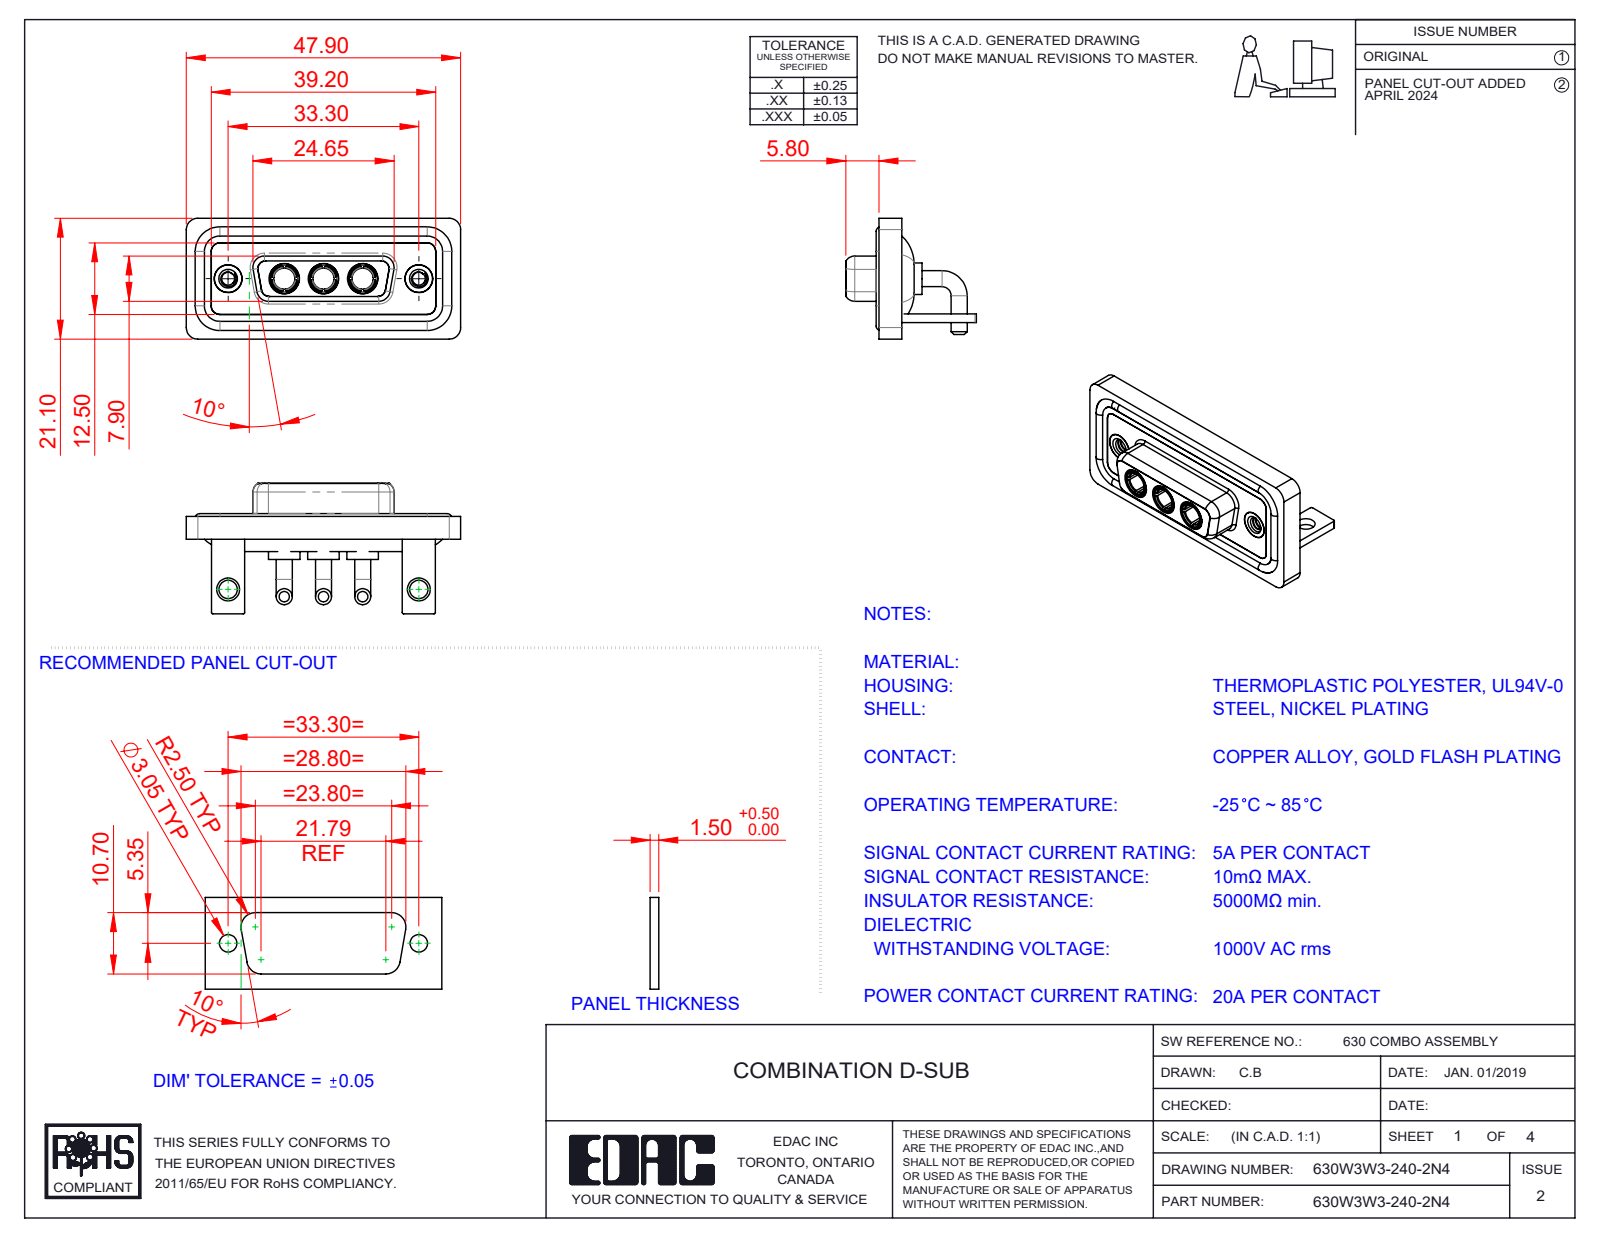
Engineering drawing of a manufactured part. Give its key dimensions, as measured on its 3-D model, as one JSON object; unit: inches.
{"part_name": "630Combo Shell Front_15 Contacts; 630Combo Threaded Rivet_2; 630Combo Housing_3W3; 630Combo Stabilizer Bracket_50 Contacts (+4 more)", "step_written_by": "SolidWorks 2023 (CONFIG_CONTROL_DESIGN)", "units": "inches", "bodies": {"solids": 15, "faces": 668, "planar": 212, "cylindrical": 287, "other": 169}, "overall_size": [1.886, 0.898, 0.831], "volume_in3": 0.399, "surface_area_in2": 16.6, "round_holes": [[0.191, 5], [0.146, 3], [0.209, 3], [0.089, 2], [0.126, 2], [0.157, 2], [0.159, 2], [0.197, 2]], "round_bosses_or_shafts": [[0.11, 6], [0.063, 4], [0.217, 3], [0.205, 3], [0.195, 3], [0.187, 3], [0.148, 3], [0.195, 2]], "partial_cylinders_radius": [[0.079, 21], [0.059, 18], [0.01, 16], [0.053, 12], [0.063, 8], [0.02, 5], [0.024, 4], [0.026, 4]], "face_to_face_distances": [0.016, 0.114, 0.059, 0.071, 0.146, 0.043, 0.161, 0.063, 0.098, 0.055], "hole_center_spacings": [0.27, 0.386, 0.656, 0.925, 1.311, 0.539]}
